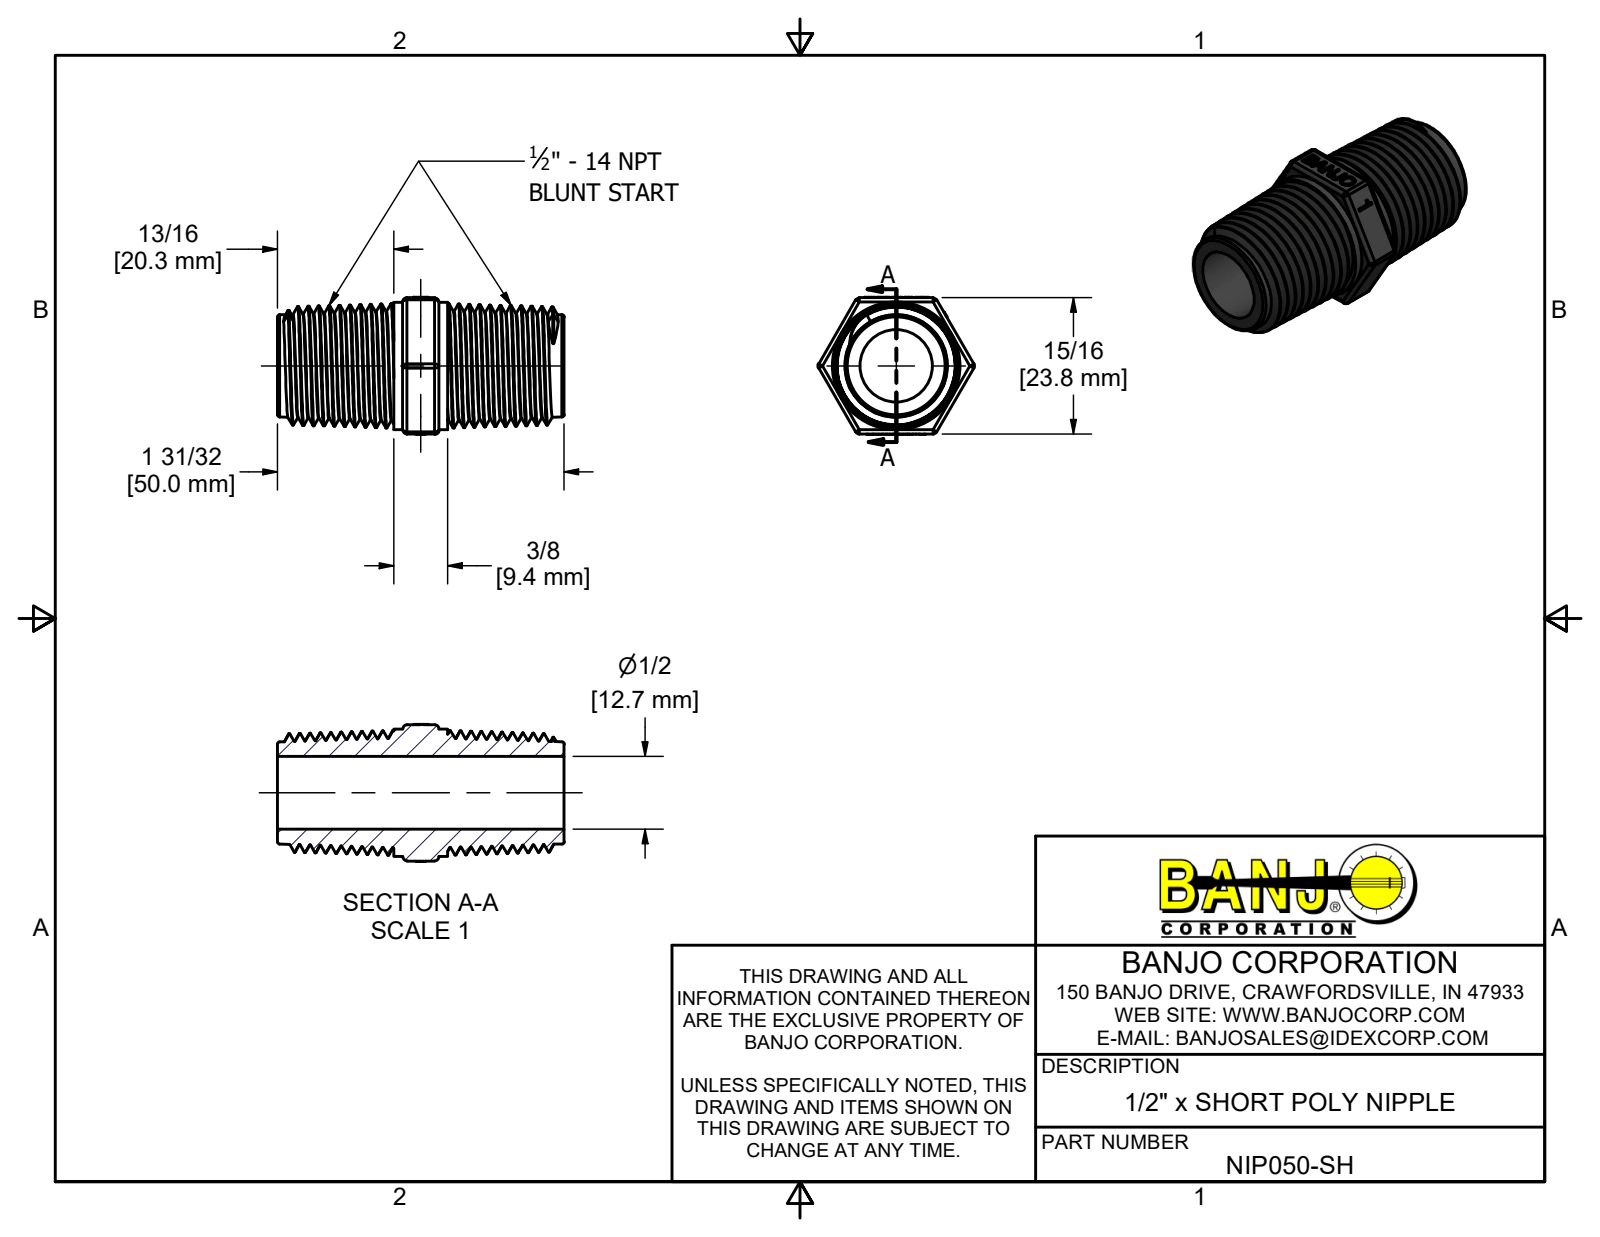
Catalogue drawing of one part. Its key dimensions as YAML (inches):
part_name: "NIP050-SH; NIP050-SHU"
step_written_by: "Autodesk Inventor 2022 (AUTOMOTIVE_DESIGN)"
units: inches
bodies: {solids: 1, faces: 274, planar: 125, cylindrical: 21, other: 128}
overall_size: [1.97, 1.073, 0.944]
volume: 0.631
surface_area: 11.99
round_holes:
  - {diameter: 0.5, count: 1}
round_bosses_or_shafts:
  - {diameter: 0.875, count: 1}
partial_cylinders:
  - {radius: 0.03, count: 18}
face_to_face_distances: [0.938, 0.8, 1.17, 1.97, 0.86, 1.11, 0.06, 0.31, 0.37, 0.25]
